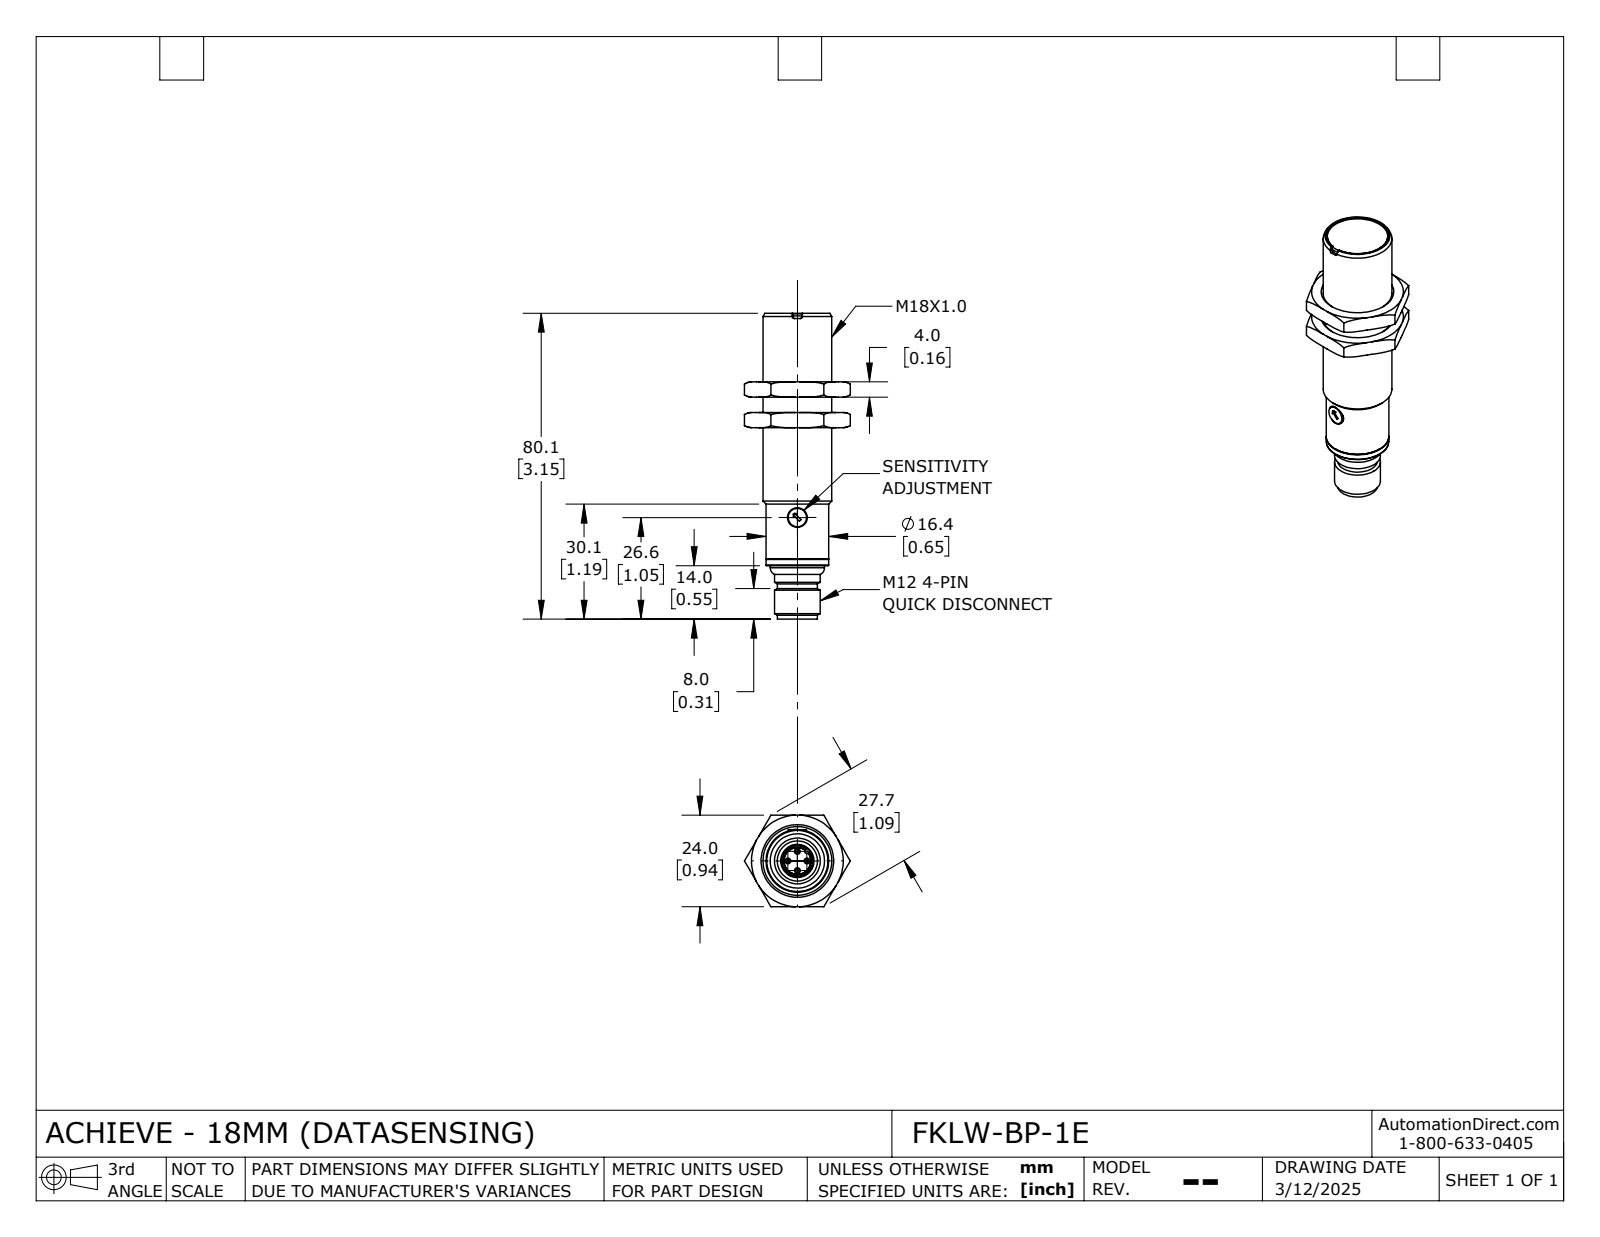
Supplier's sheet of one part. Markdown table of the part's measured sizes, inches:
| quantity | value |
| --- | --- |
| part name | FKLW-BP-1E_Default |
| STEP written by | SolidWorks 2024 (CONFIG_CONTROL_DESIGN) |
| units | inches |
| bodies | 4 solids, 135 faces (54 planar, 29 cylindrical, 52 other) |
| overall size | 3.154 × 1.091 × 0.945 |
| volume | 1.259 in³ |
| surface area | 12.98 in² |
| round holes (diameter × count) | 0.106 × 1, 0.185 × 1, 0.278 × 1, 0.327 × 1, 0.622 × 1, 0.709 × 1 |
| round bosses / shafts (diameter × count) | 0.039 × 4, 0.646 × 1, 0.559 × 1, 0.472 × 1, 0.413 × 1, 0.276 × 1, 0.189 × 1 |
| partial cylindrical surfaces (radius × count) | 0.02 × 4, 0.024 × 1, 0.331 × 1 |
| main face-to-face distances | 0.157, 0.315, 0.945, 0.472, 0.055, 0.348, 0.403, 0.612, 0.96, 1.015 |
